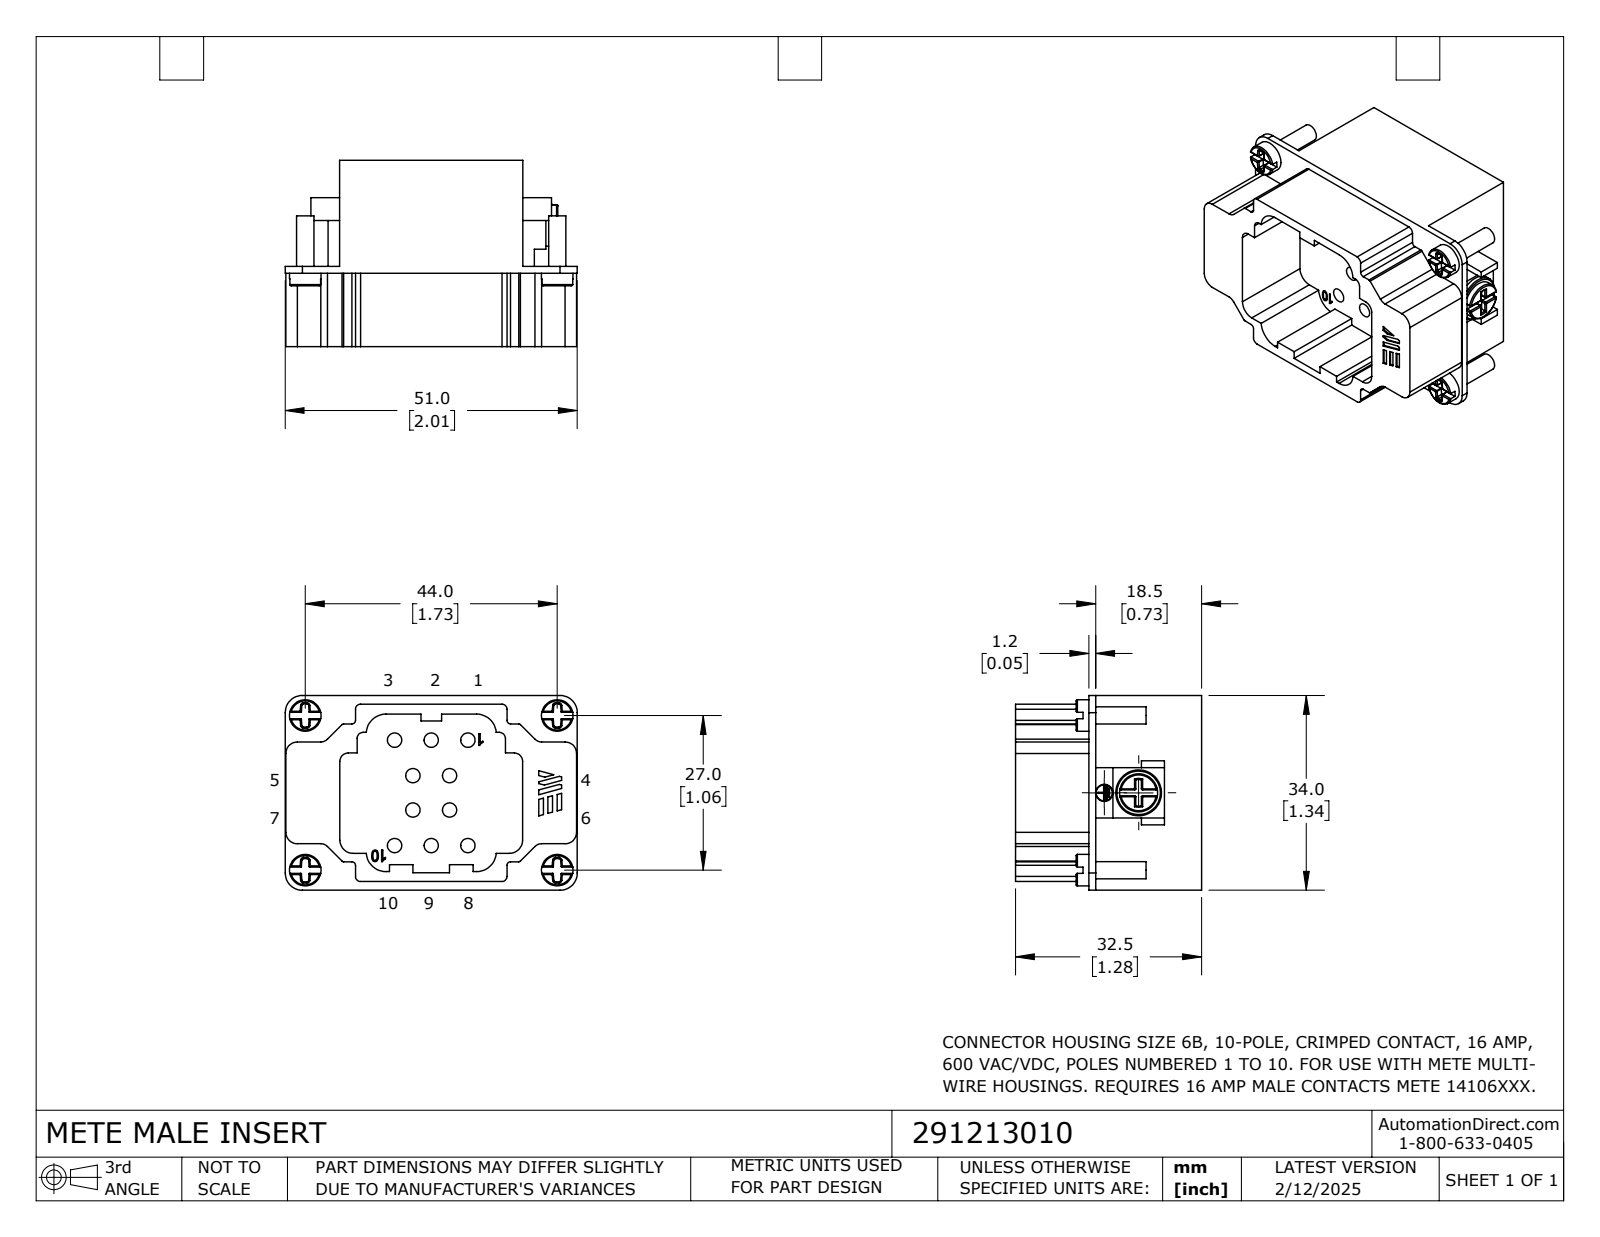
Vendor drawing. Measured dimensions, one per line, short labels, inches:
name: 291213010
written by: SolidWorks 2024 (CONFIG_CONTROL_DESIGN)
unit: in
bodies: 1 solid, 484 faces (230 planar, 160 cylindrical, 94 other)
size: 2.008 × 1.339 × 1.28
volume: 1.606 in³; area: 20.04 in²
holes: 10× ⌀0.098, 10× ⌀0.177, 1× ⌀0.118, 1× ⌀0.157
bosses: 4× ⌀0.217, 4× ⌀0.118, 1× ⌀0.315, 1× ⌀0.261, 1× ⌀0.11
rounds: 36× R0.008, 4× R0.015, 4× R0.024, 4× R0.035, 4× R0.064, 4× R0.079, 4× R0.118, 4× R0.136
face distances: 1.339, 0.72, 0.06, 1.279, 0.559, 0.728, 0.047, 1.26, 1.28, 0.551
hole spacings: 0.275, 0.496, 0.252, 0.45, 0.611, 0.767, 0.236, 0.724
